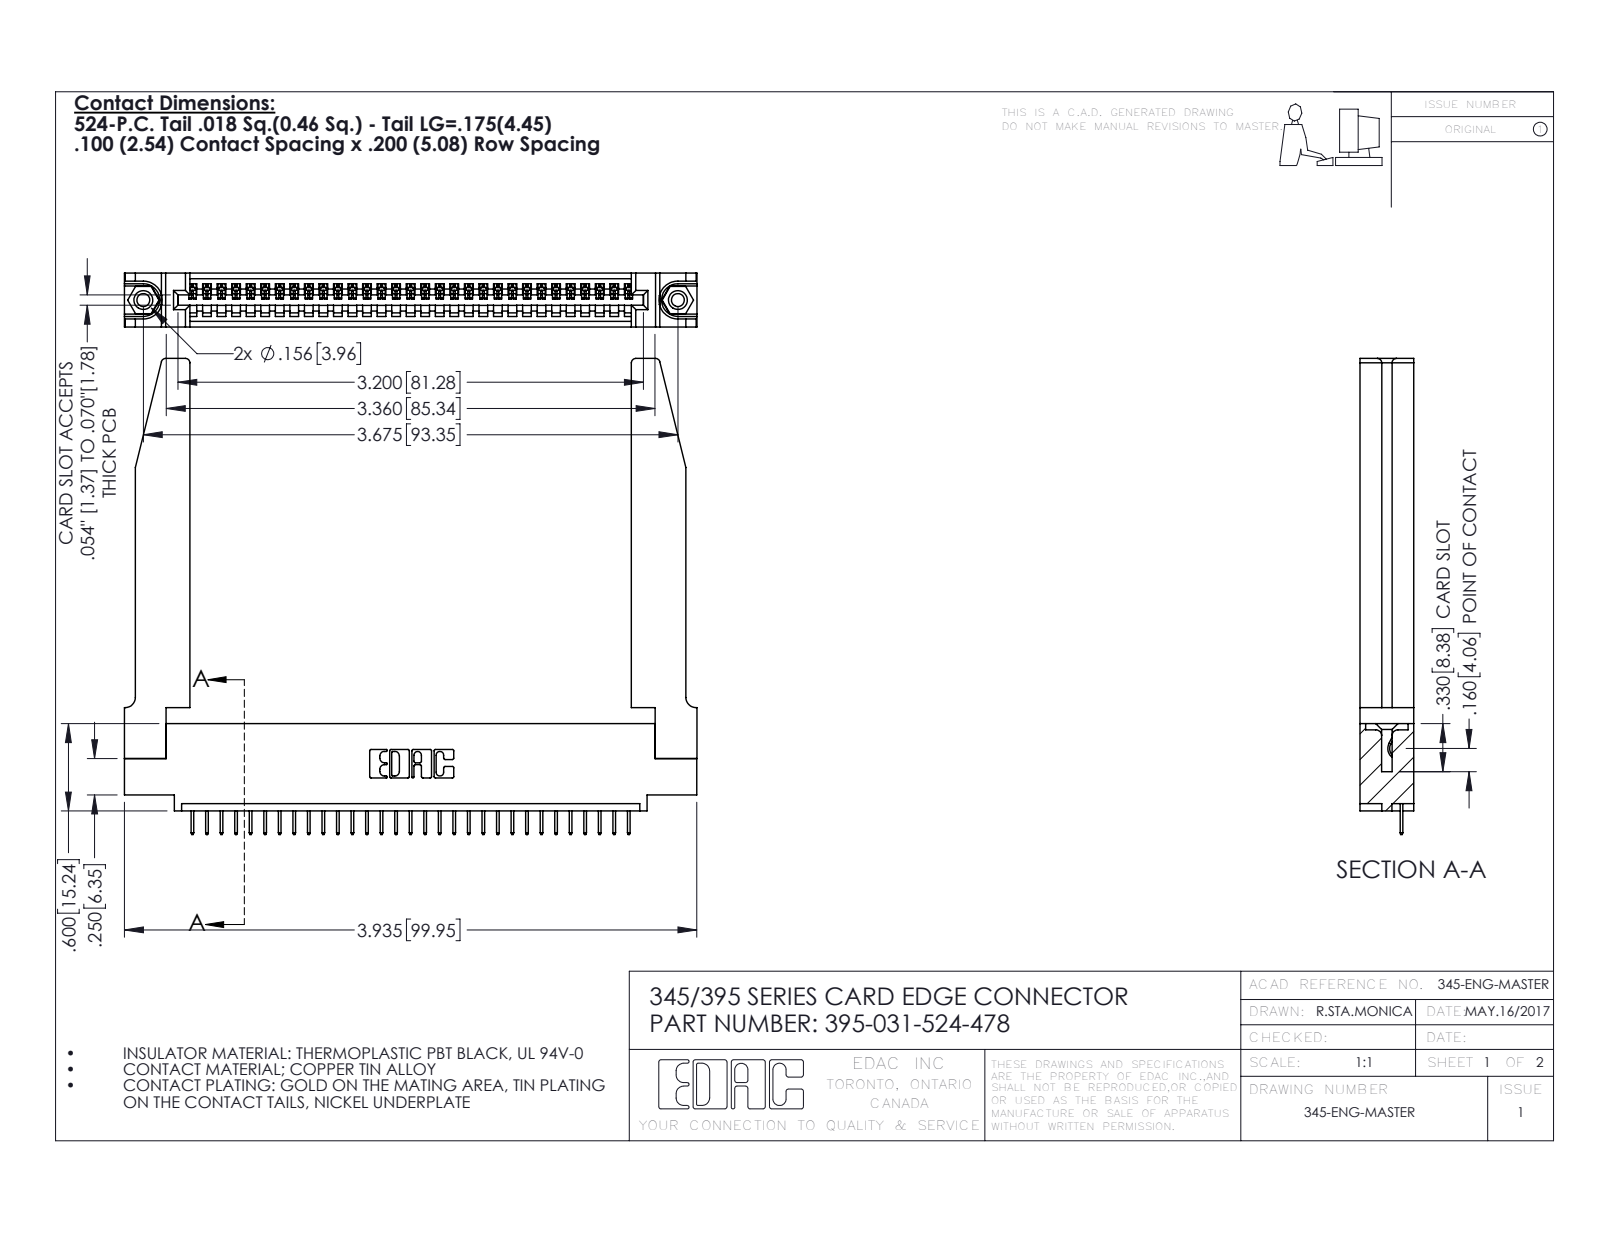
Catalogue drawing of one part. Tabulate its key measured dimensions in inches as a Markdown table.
| quantity | value |
| --- | --- |
| part name | 345 Part_0.110 Offset - 0.156 Dia-TH; 395-031-524-478; 345-250-001_345-250-001-102; 345-292-001_345-293-124 (+1 more) |
| STEP written by | SolidWorks 2016 (CONFIG_CONTROL_DESIGN) |
| units | inches |
| bodies | 36 solids, 2286 faces (1652 planar, 582 cylindrical, 52 other) |
| overall size | 3.936 × 3.272 × 0.37 |
| volume | 1.036 in³ |
| surface area | 28.87 in² |
| round holes (diameter × count) | 0.089 × 2, 0.125 × 2, 0.156 × 2, 0.064 × 1 |
| round bosses / shafts (diameter × count) | 0.155 × 2 |
| partial cylindrical surfaces (radius × count) | 0.006 × 62, 0.01 × 22, 0.03 × 8, 0.007 × 6, 0.031 × 6, 0.026 × 3, 0.031 × 2, 0.04 × 2 |
| main face-to-face distances | 0.37, 0.072, 0.298, 0.2, 0.098, 0.272, 0.025, 0.15, 0.148, 0.225 |
| hole center spacings | 0.27, 3.44, 3.675 |
